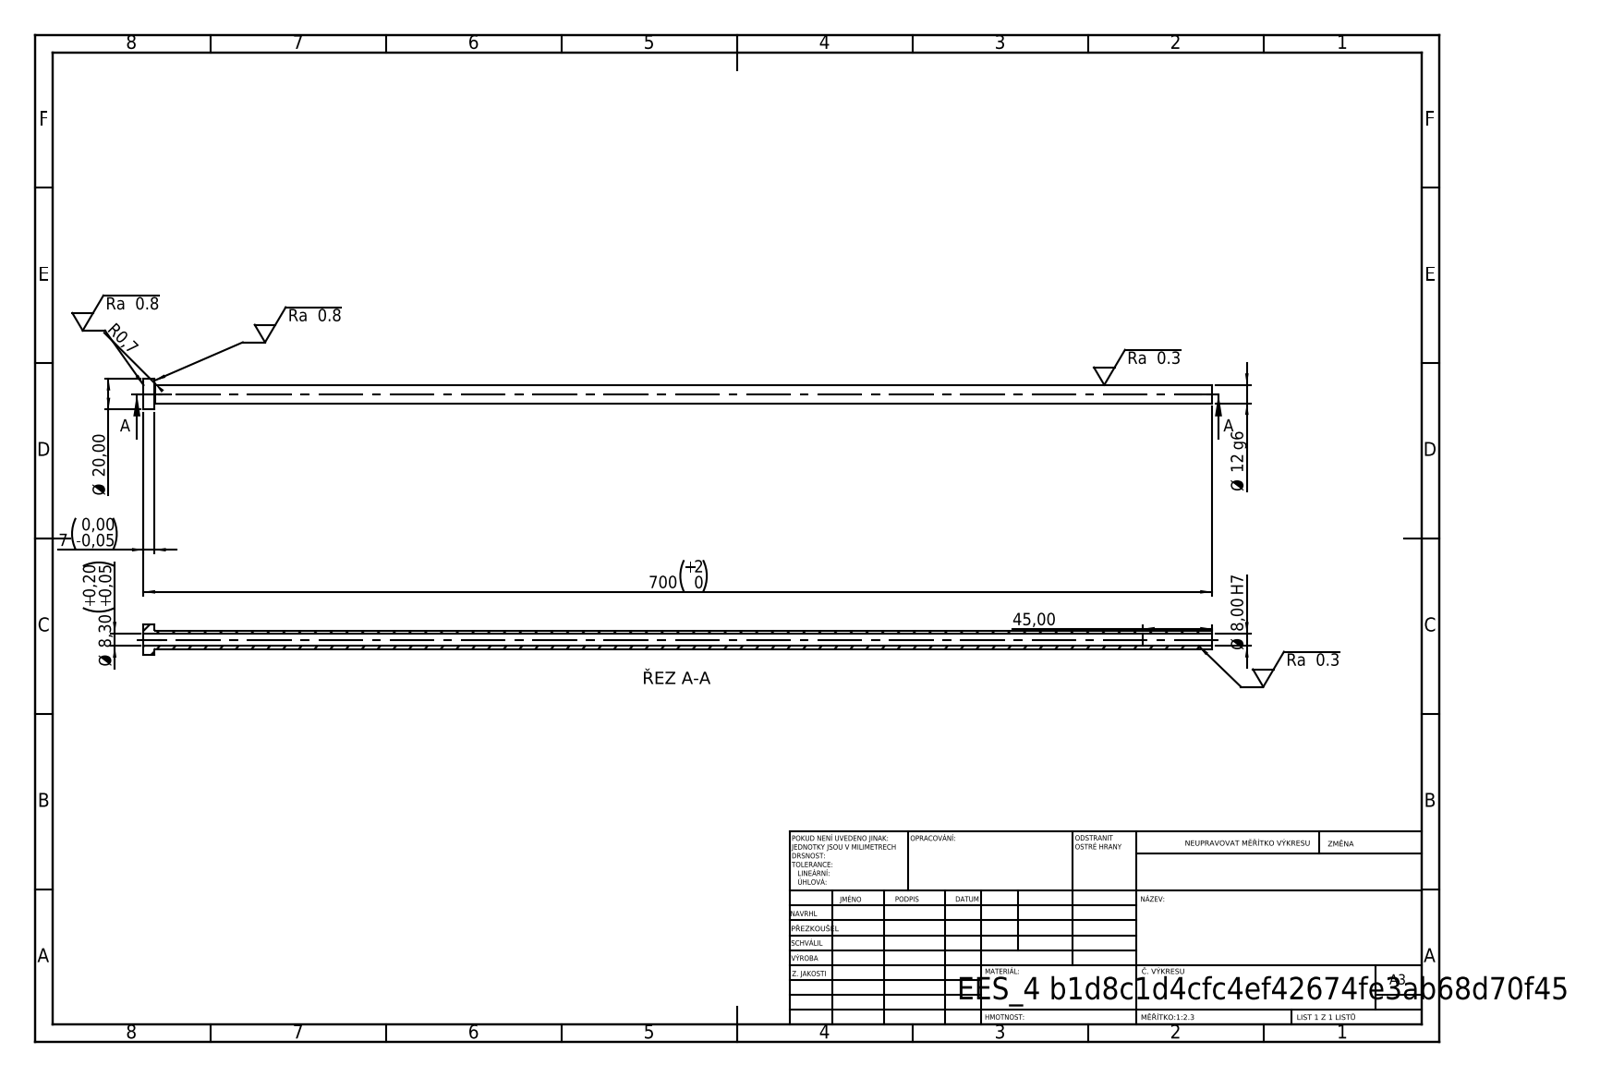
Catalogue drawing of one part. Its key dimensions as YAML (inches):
step_written_by: "SolidWorks 2019 (CONFIG_CONTROL_DESIGN)"
units: inches
bodies: {solids: 1, faces: 14, planar: 4, cylindrical: 8, other: 2}
overall_size: [27.559, 0.787, 0.787]
volume: 2.617
surface_area: 70.2
round_holes:
  - {diameter: 0.315, count: 1}
  - {diameter: 0.327, count: 1}
round_bosses_or_shafts:
  - {diameter: 0.787, count: 1}
  - {diameter: 0.472, count: 1}
face_to_face_distances: [0.276, 27.559, 27.283, 25.787, 25.512, 1.772]
